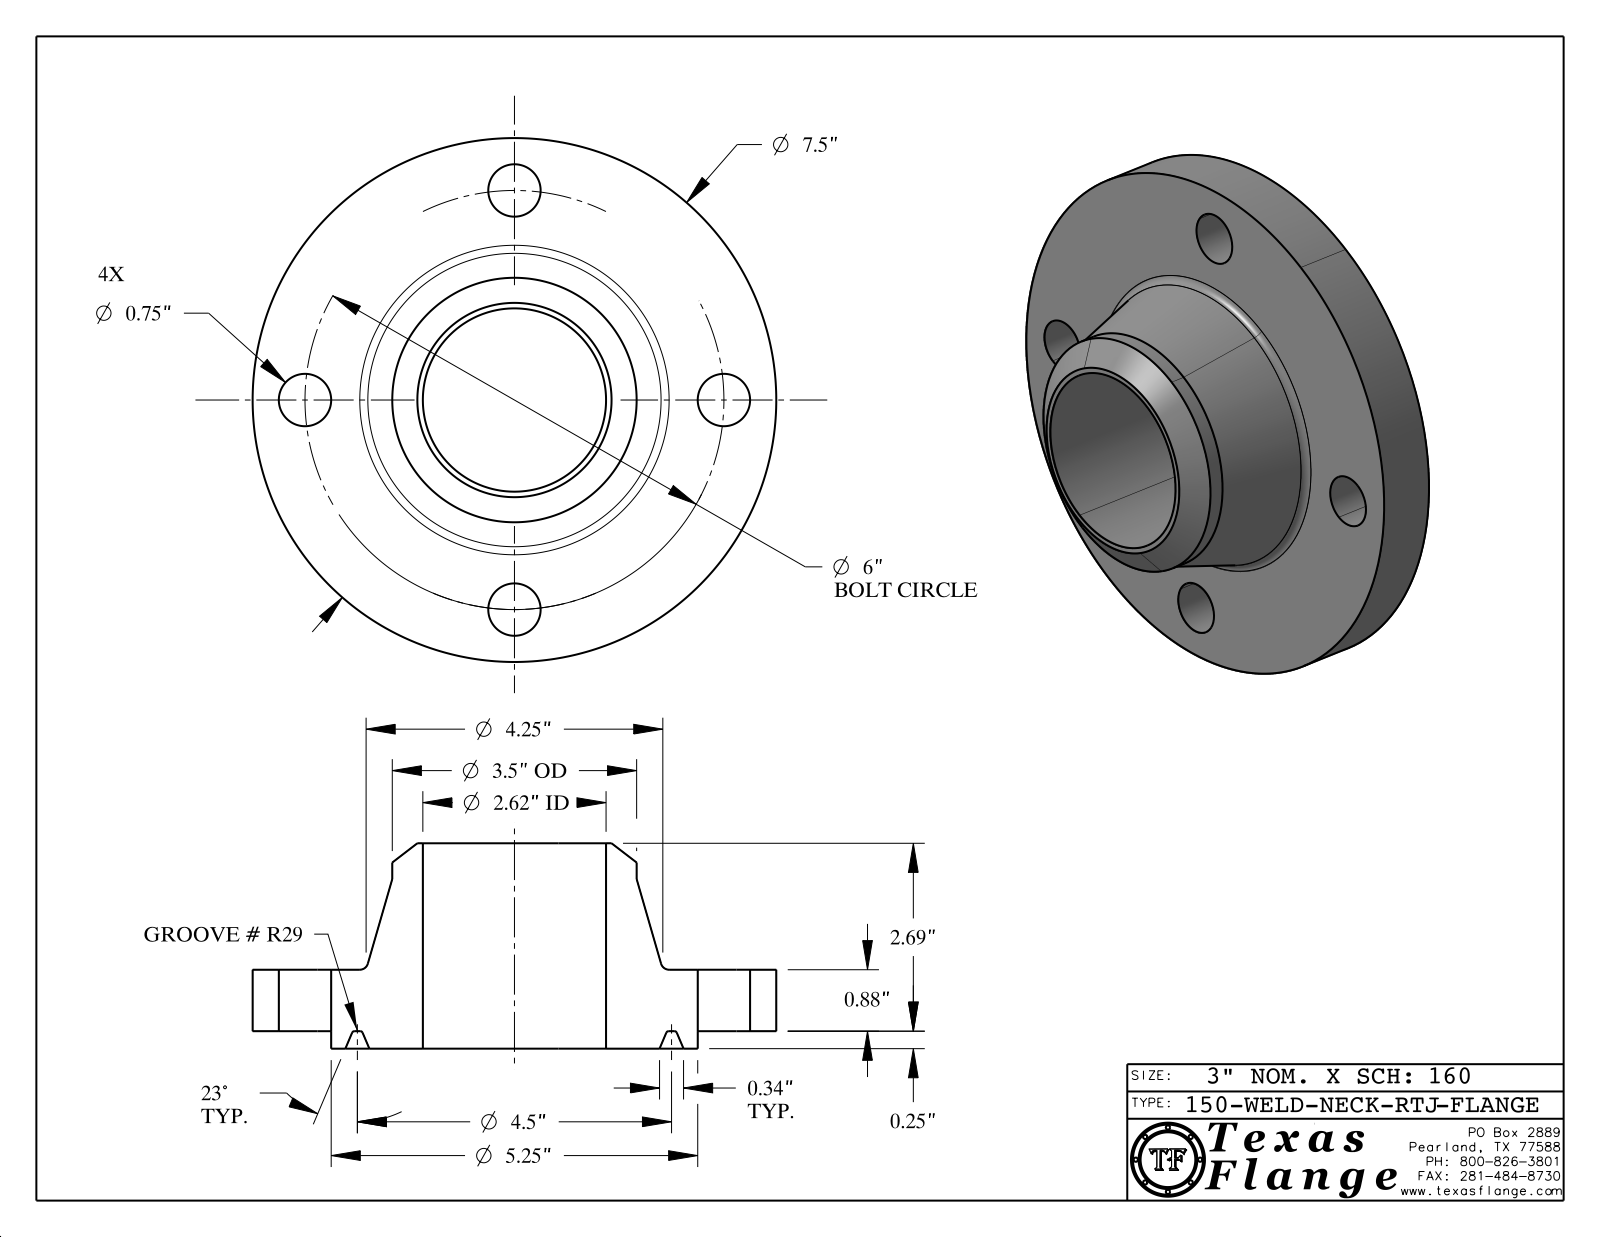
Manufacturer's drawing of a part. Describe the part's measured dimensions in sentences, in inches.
The part is named "150-WELD-NECK-RTJ". Its 3-D file was written by "CATIA V5 STEP AP214 (AUTOMOTIVE_DESIGN)". It is 1 solid with 421 faces: 371 planar, 36 cylindrical and 14 other. Overall it measures 7.5 by 7.5 by 2.94 inches. Its volume is 45.79 cubic inches and its surface area 151 square inches. Round holes: 4 of diameter 0.75, 1 of diameter 0.495, 1 of diameter 2.624. Round bosses or shafts: 8 of diameter 0.03, 1 of diameter 7.5, 1 of diameter 5.25, 1 of diameter 3.5, 1 of diameter 0.39. The main face-to-face distances are 0.88, 0.25, 1.13, 2.94, 2.69, 1.81, 1.125, 0.875, 1.815, 0.148. The hole center spacings are 3, 4.243, 2.296, 5.543, 6.
